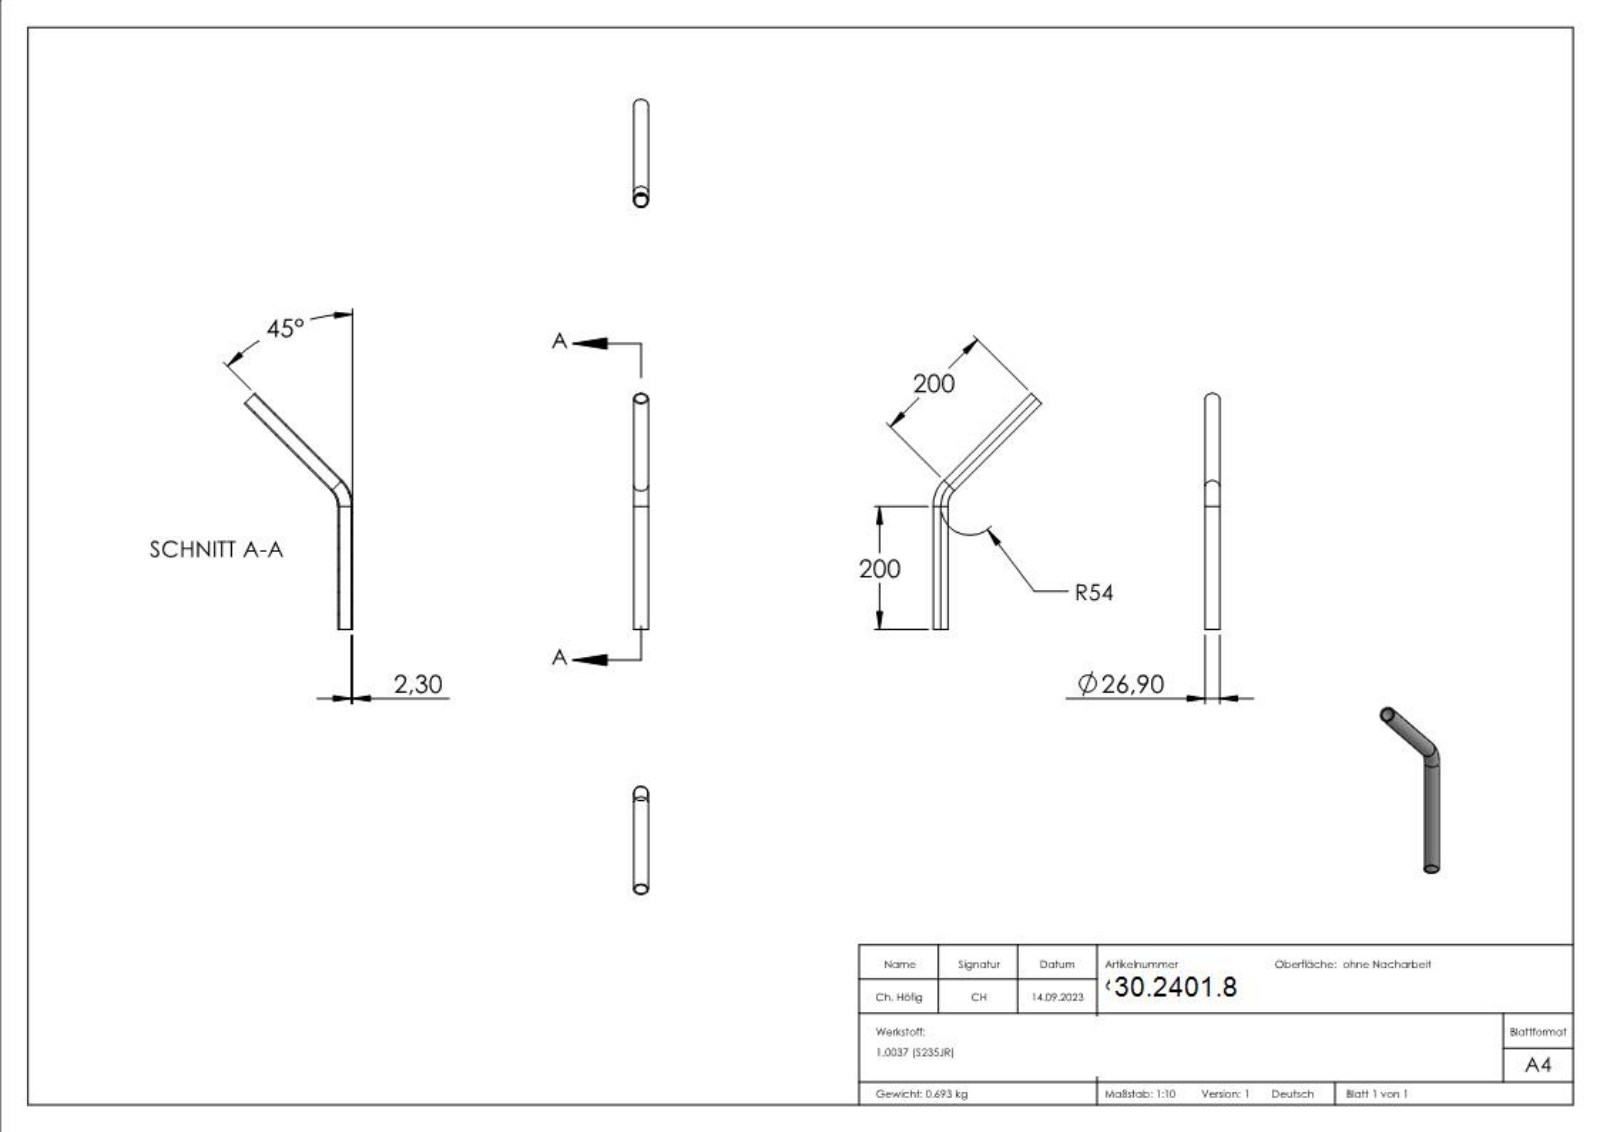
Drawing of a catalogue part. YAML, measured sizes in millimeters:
part_name: "6965-045"
step_written_by: "SolidWorks 2018 (CONFIG_CONTROL_DESIGN)"
units: millimeters
bodies: {solids: 1, faces: 224, planar: 118, cylindrical: 4, other: 102}
overall_size: [438.27, 200.56, 26.9]
volume: 88876
surface_area: 77642
round_holes:
  - {diameter: 22.3, count: 2}
round_bosses_or_shafts:
  - {diameter: 26.9, count: 2}
face_to_face_distances: [0.53, 0.58, 0.34, 0.39, 0.32, 0.48, 0.31, 0.35, 0.4, 0.54]
